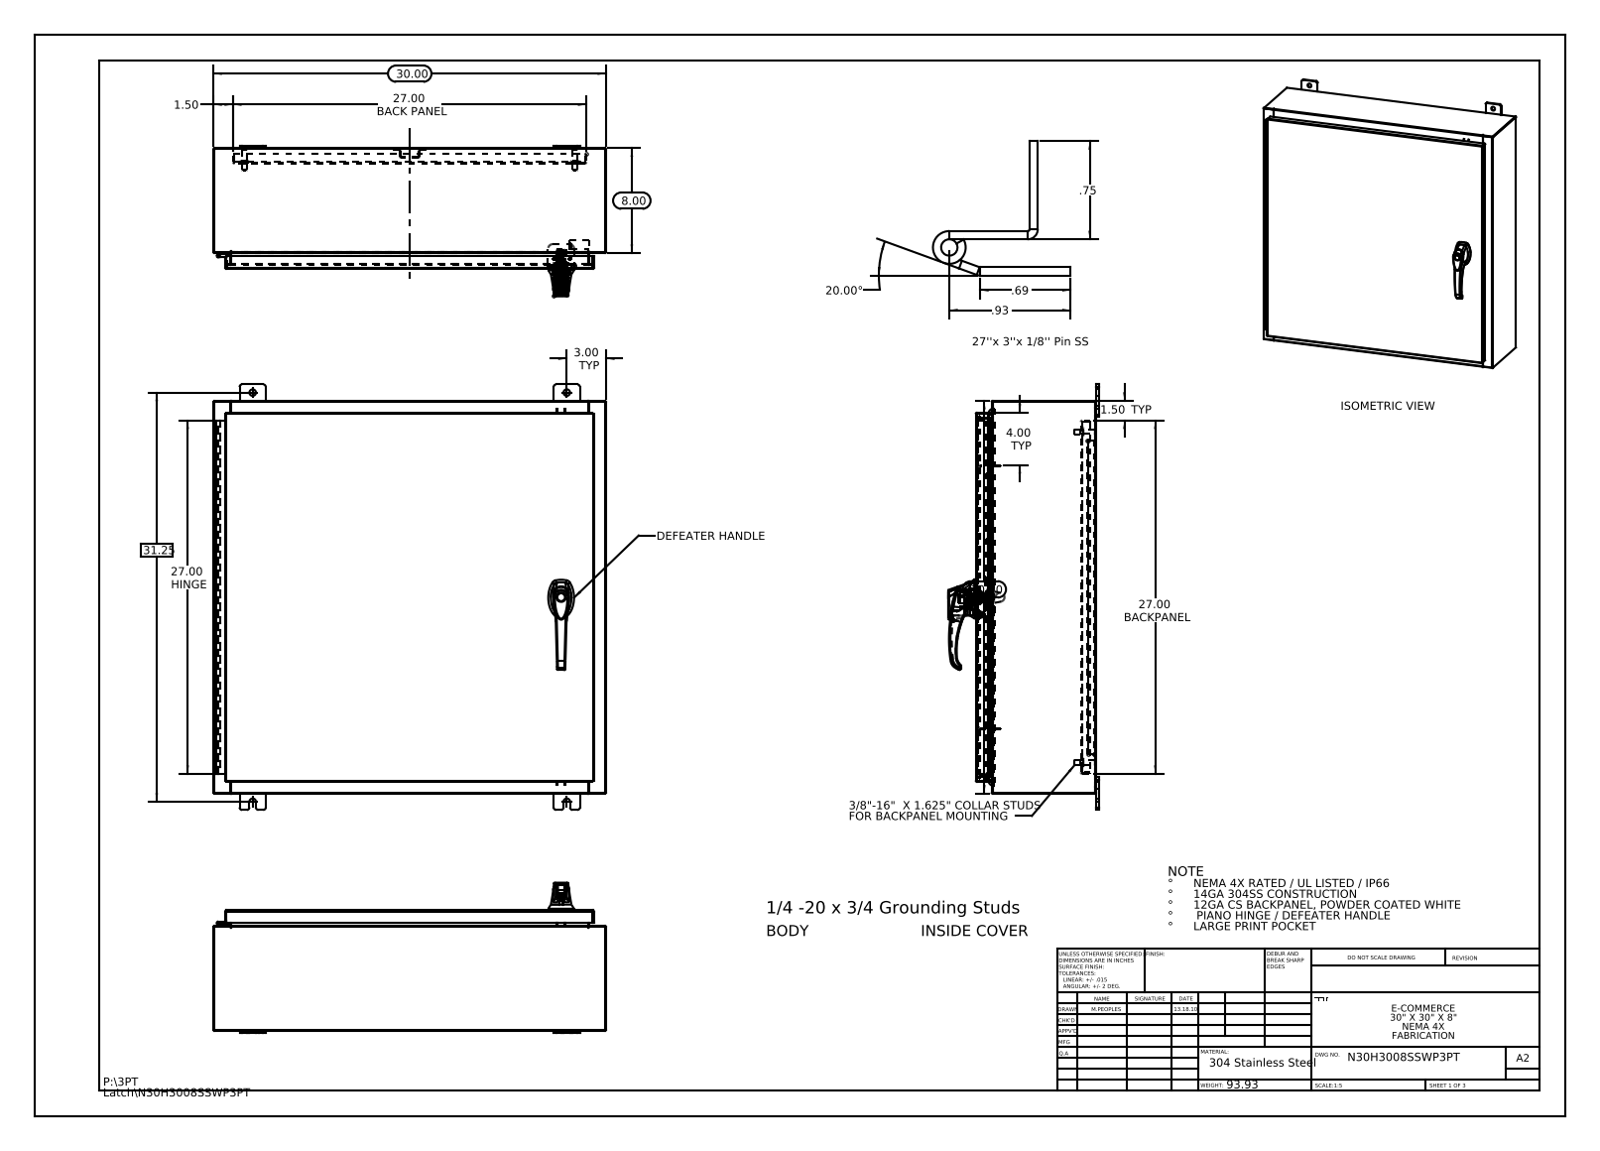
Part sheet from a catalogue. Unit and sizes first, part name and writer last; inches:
Units: inches
Overall size (bounding box): 32.5 × 30 × 11.495
Round holes (diameter × count): ⌀0.5 ×8, ⌀0.25 ×4, ⌀0.138 ×3, ⌀0.161 ×3, ⌀0.079 ×2, ⌀0.203 ×2, ⌀0.313 ×2, ⌀0.437 ×2, ⌀0.125 ×1, ⌀0.125 ×1, ⌀0.197 ×1, ⌀0.276 ×1
Round bosses / shafts (diameter × count): ⌀0.625 ×4, ⌀0.375 ×4, ⌀0.33 ×4, ⌀1.181 ×1, ⌀0.748 ×1, ⌀0.68 ×1, ⌀0.661 ×1, ⌀0.639 ×1
Partial cylindrical surfaces — rounded edges, fillets, slot ends (radius × count): R0.118 ×37, R0.006 ×33, R0.013 ×28, R0.19 ×24, R0.088 ×22, R0.039 ×15, R0.028 ×12, R0.008 ×6
Main face-to-face distances: 0.075, 9.126, 29.925, 9.051, 0.104, 9.201, 1, 8.126, 1.075, 8.051
Hole centre spacings: 8.369, 0.295, 0.625, 0.841, 1.25, 1.313, 1.561, 1.858
Volume: 332.1 in³ · Surface area: 8 196 in²
Bodies: 32 solids, 2614 faces (983 planar, 977 cylindrical, 654 other)
Part name (STEP PRODUCT): g26103103_26163303; N30H3008SSWP3PT Mounting Studs; NMP-SS-RODGUIDES; 033060_032151 (+8 more)
STEP written by: SolidWorks 2013 (CONFIG_CONTROL_DESIGN)
